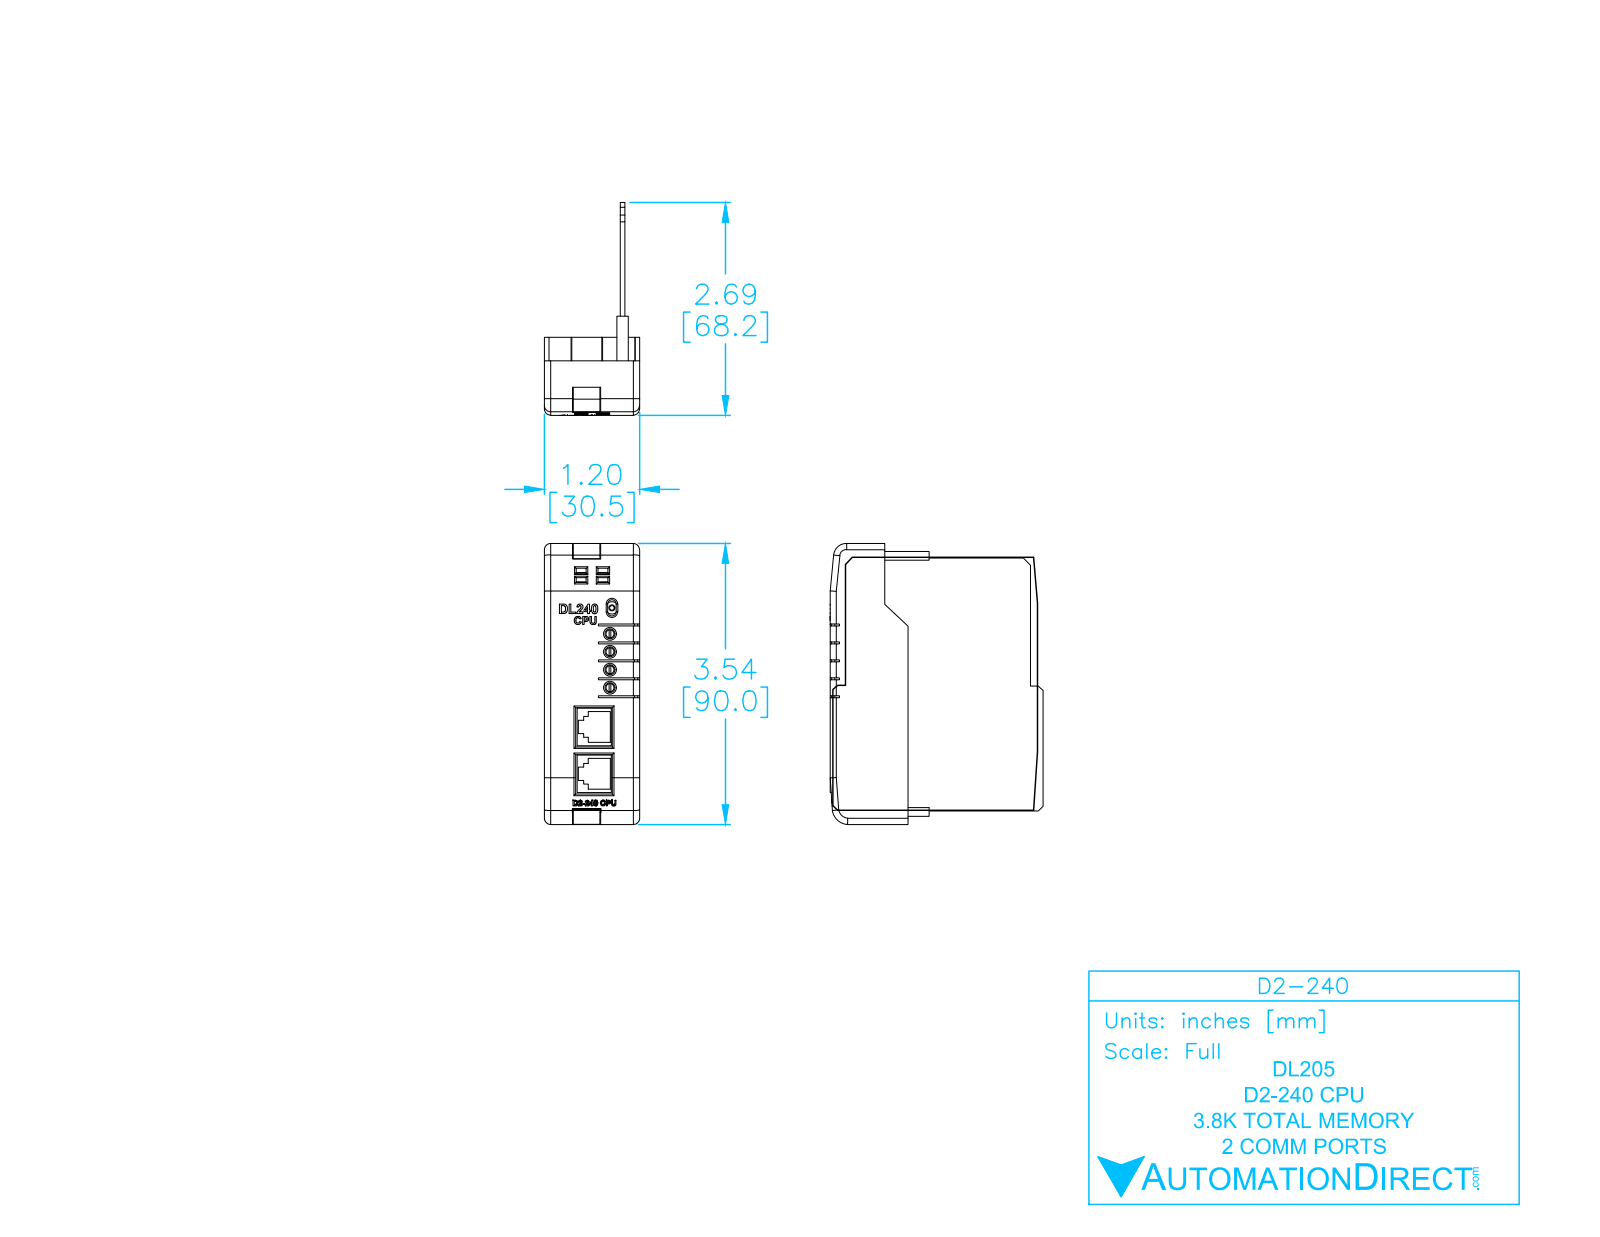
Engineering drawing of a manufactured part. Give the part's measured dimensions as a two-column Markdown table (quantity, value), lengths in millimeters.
| quantity | value |
| --- | --- |
| part name | D2-240_CPU_Light_NEW |
| STEP written by | SolidWorks 2009 (AUTOMOTIVE_DESIGN) |
| units | millimeters |
| bodies | 12 solids, 662 faces (403 planar, 111 cylindrical, 148 other) |
| overall size | 90 × 68.21 × 30.5 |
| volume | 21 126 mm³ |
| surface area | 31 970 mm² |
| round holes (diameter × count) | 3.15 × 4 |
| round bosses / shafts (diameter × count) | 2.63 × 4, 4 × 1, 2 × 1 |
| partial cylindrical surfaces (radius × count) | 0.5 × 31, 2 × 10, 0.25 × 4, 1 × 2, 1.36 × 2, 2.62 × 1, 3.79 × 1, 4.12 × 1 |
| main face-to-face distances | 1.5, 4.72, 24.28, 29, 3.22, 25.78, 30.5, 6.22, 22.78, 27.5 |
| hole center spacings | 5.75, 11.5, 17.25 |
